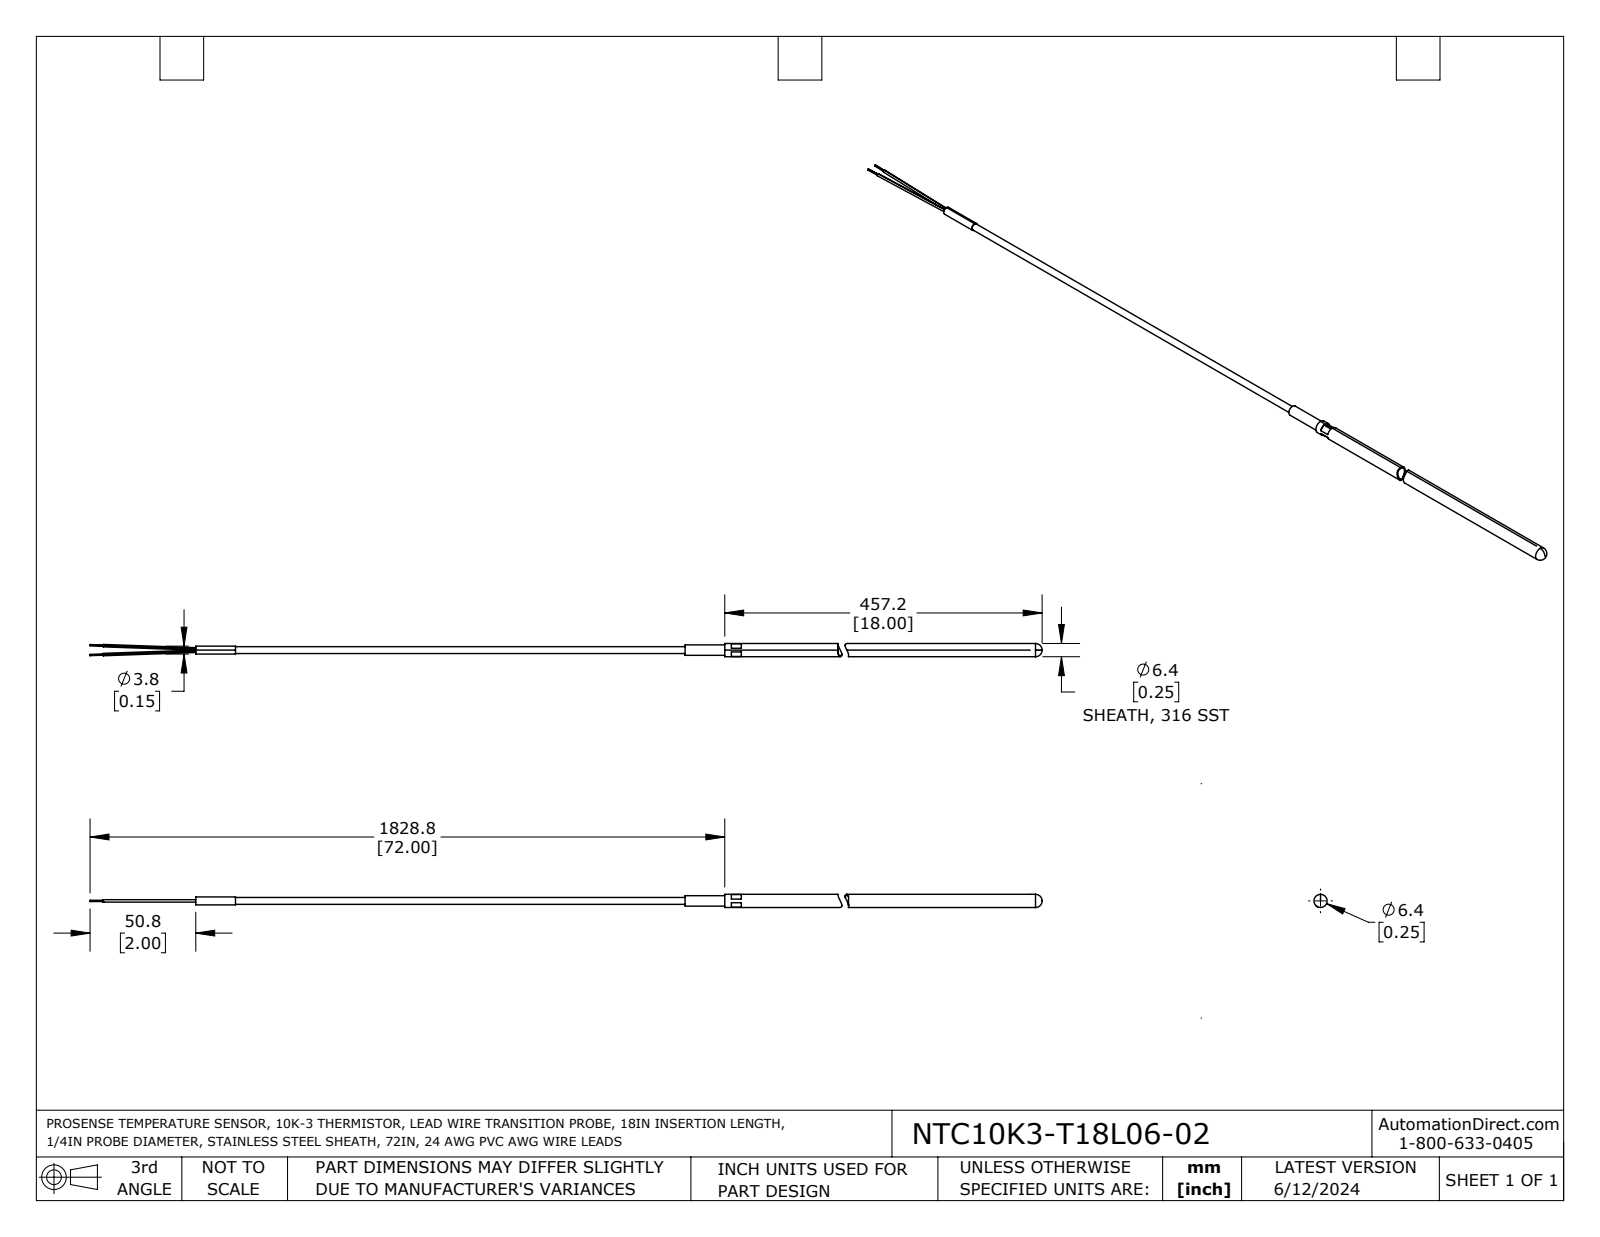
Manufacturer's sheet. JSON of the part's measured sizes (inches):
{"part_name": "NTC10K3-T18L06-02", "step_written_by": "SolidWorks 2021 (AUTOMOTIVE_DESIGN)", "units": "inches", "bodies": {"solids": 3, "faces": 49, "planar": 25, "cylindrical": 14, "other": 10}, "overall_size": [29.995, 0.25, 0.25], "volume_in3": 0.411, "surface_area_in2": 33.07, "round_holes": [[0.131, 1], [0.187, 1], [0.21, 1]], "round_bosses_or_shafts": [[0.25, 1], [0.197, 1], [0.15, 1], [0.13, 1]], "face_to_face_distances": [0.219, 17.775, 10.001, 27.776, 0.75, 10.126, 0.125, 17.65, 10.314, 0.313]}
